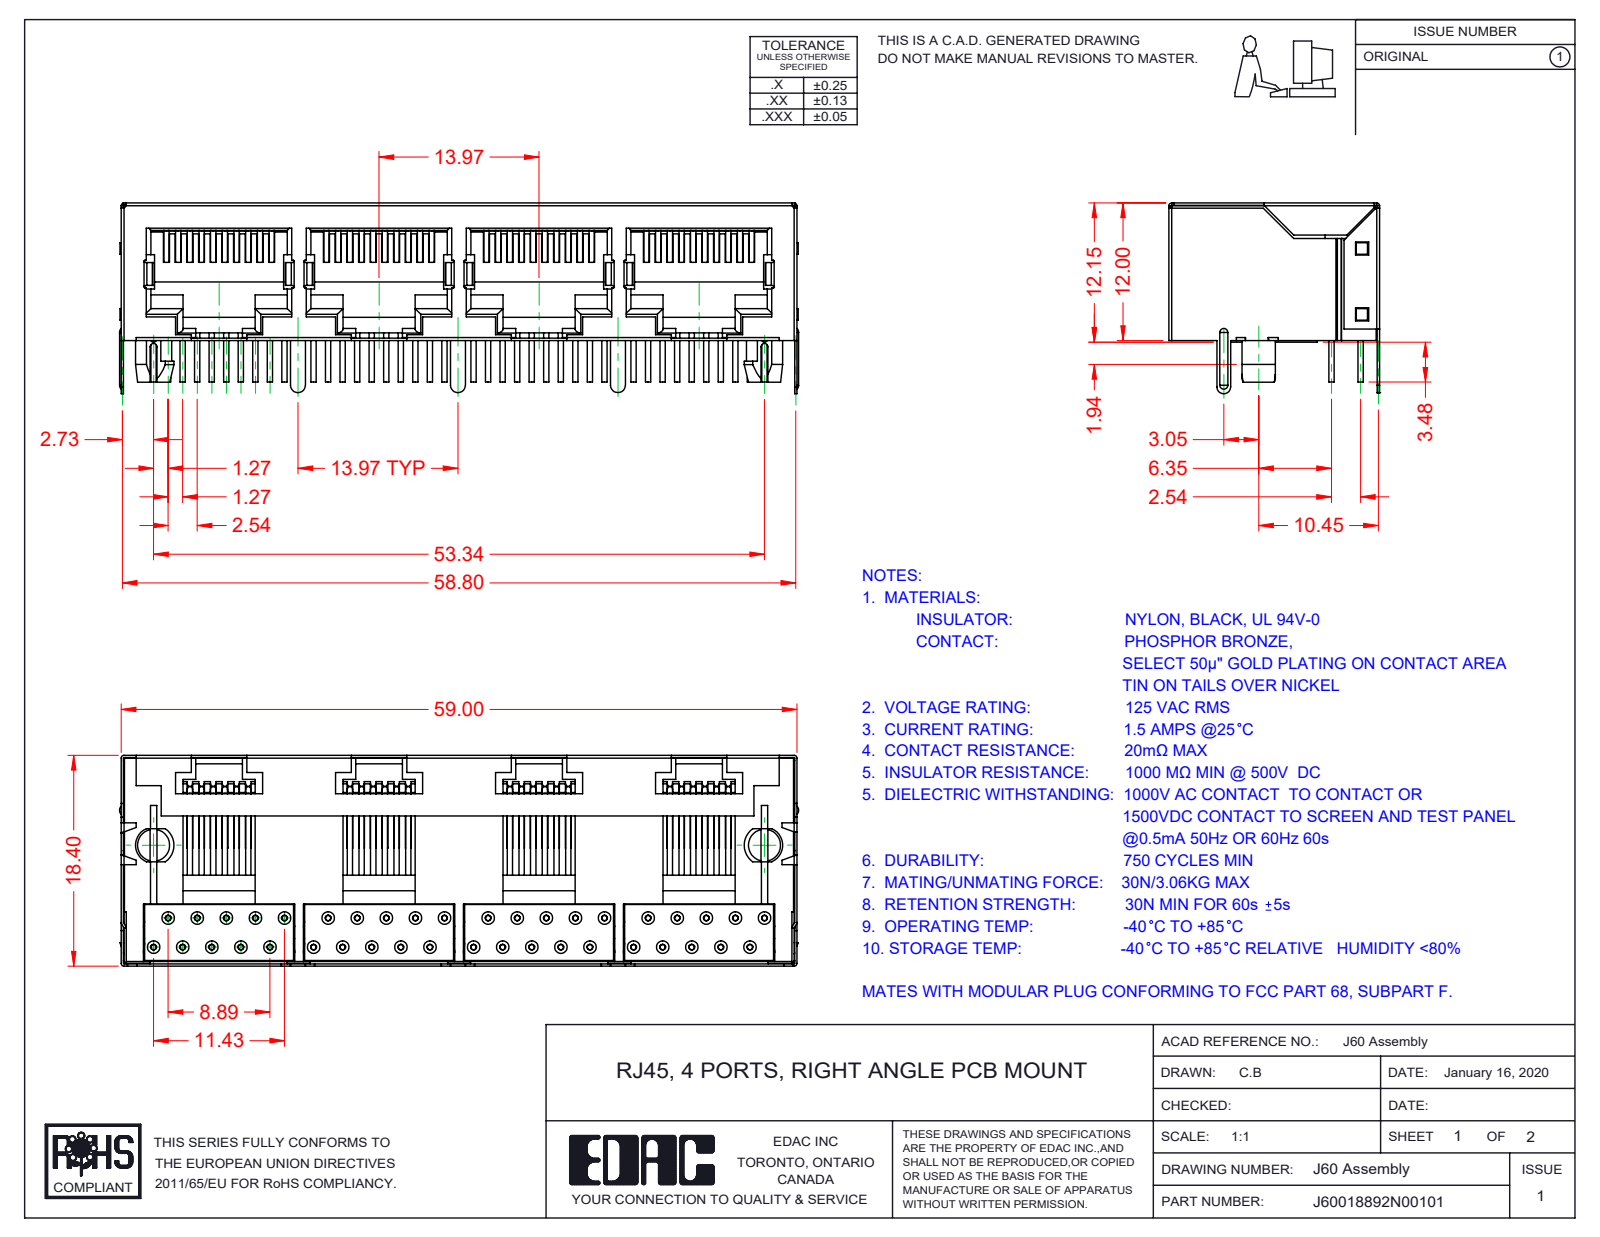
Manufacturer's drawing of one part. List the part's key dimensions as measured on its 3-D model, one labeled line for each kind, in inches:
Part name (STEP PRODUCT): 60 Contacts_10P10C; 60 Insulator; RJ60041192N00101; 60 Shield
STEP written by: SolidWorks 2016 (CONFIG_CONTROL_DESIGN)
Units: inches
Bodies: 42 solids, 2674 faces (1505 planar, 763 cylindrical, 406 other)
Overall size (bounding box): 2.335 × 0.724 × 0.656
Volume: 0.431 in³ · Surface area: 29.43 in²
Round holes (diameter × count): ⌀0.02 ×40, ⌀0.043 ×40
Round bosses / shafts (diameter × count): ⌀0.018 ×120
Partial cylindrical surfaces — rounded edges, fillets, slot ends (radius × count): R0.012 ×26, R0.01 ×21, R0.02 ×18, R0.004 ×16, R0.008 ×10, R0.031 ×7, R0.026 ×3, R0.011 ×2
Main face-to-face distances: 0.02, 0.463, 0.455, 0.55, 0.086, 0.212, 0.204, 0.192, 0.717, 0.453
Hole centre spacings: 0.112, 0.1, 0.18, 0.55, 0.2, 0.51, 0.608, 0.45
